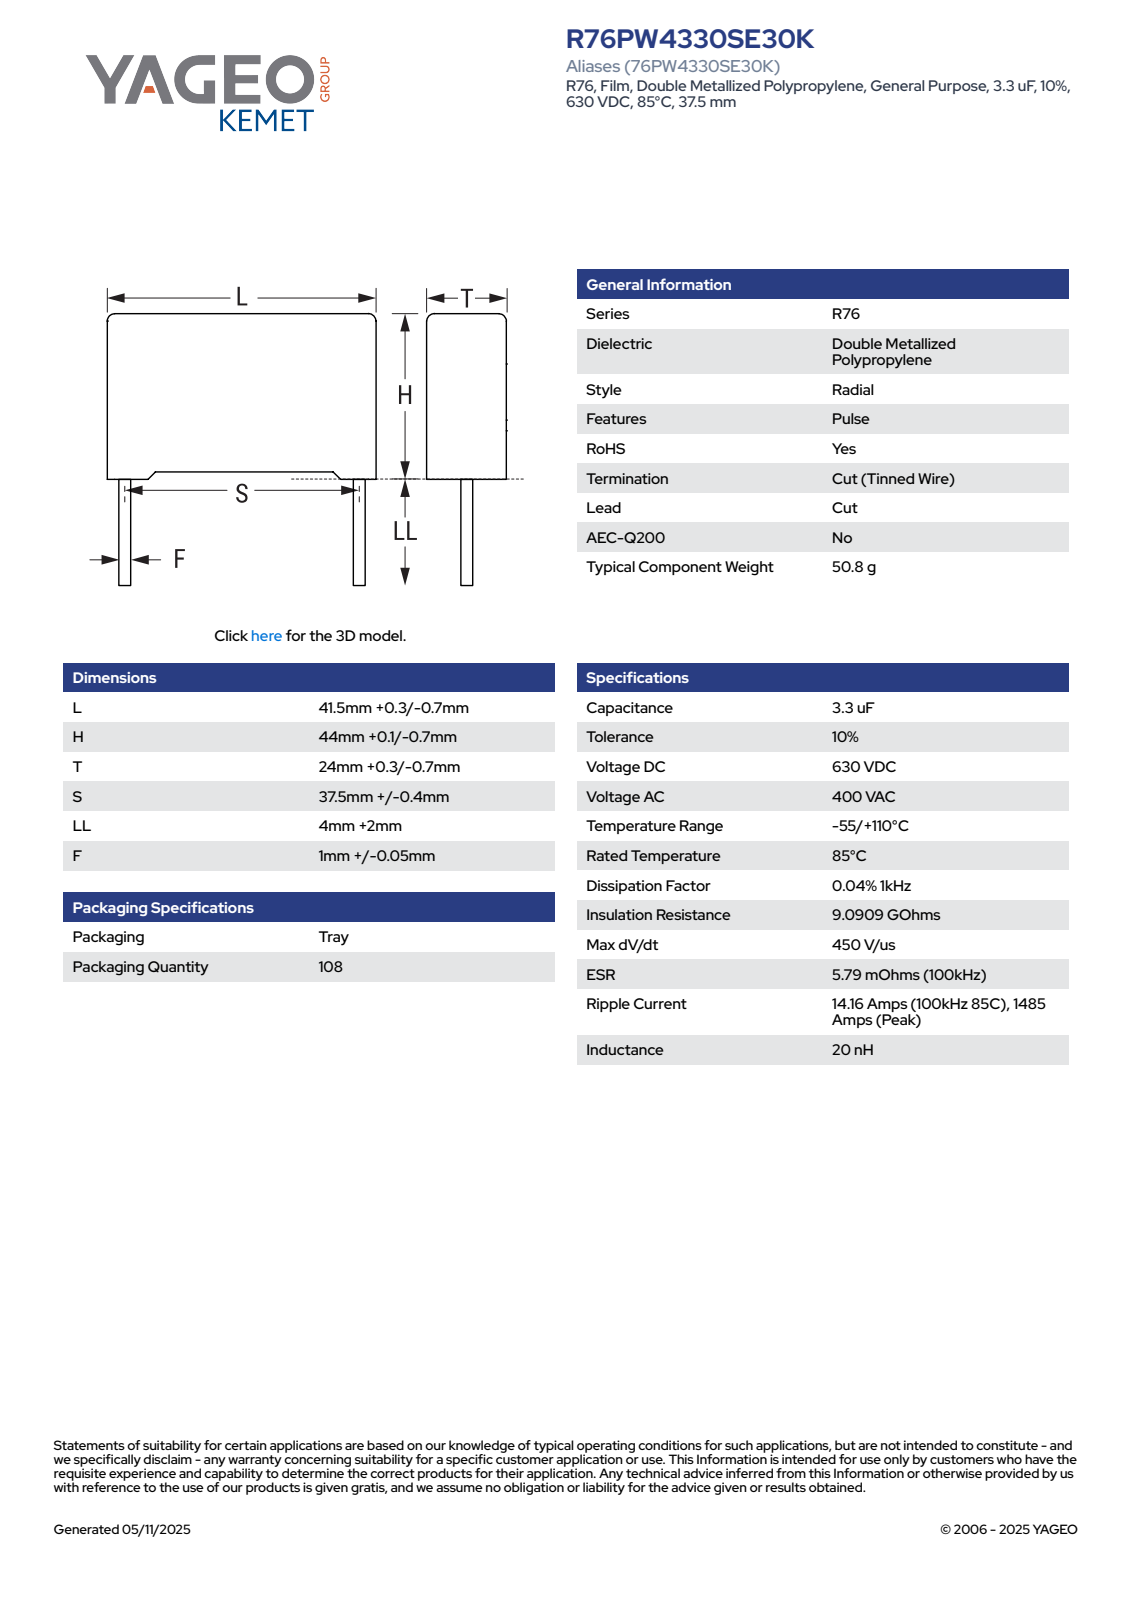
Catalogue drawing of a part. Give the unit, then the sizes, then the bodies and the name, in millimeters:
Units: millimetres
Overall size (bounding box): 50.1 × 41.8 × 24.3
Round bosses / shafts (diameter × count): ⌀1.05 ×2
Partial cylindrical surfaces — rounded edges, fillets, slot ends (radius × count): R0.5 ×4
Main face-to-face distances: 24.3, 41.8, 42.58, 0.77, 43.35, 0.75, 1.52, 44.1, 1.39, 40.41
Volume: 43 485 mm³ · Surface area: 7 967 mm²
Bodies: 4 solids, 85 faces (77 planar, 8 cylindrical, 0 other)
Part name (STEP PRODUCT): CFR_RB2_41.5X44X24_L41.8H44.1T24.3S37.5LL6F1.05
STEP written by: SolidWorks 2021 (AUTOMOTIVE_DESIGN)
